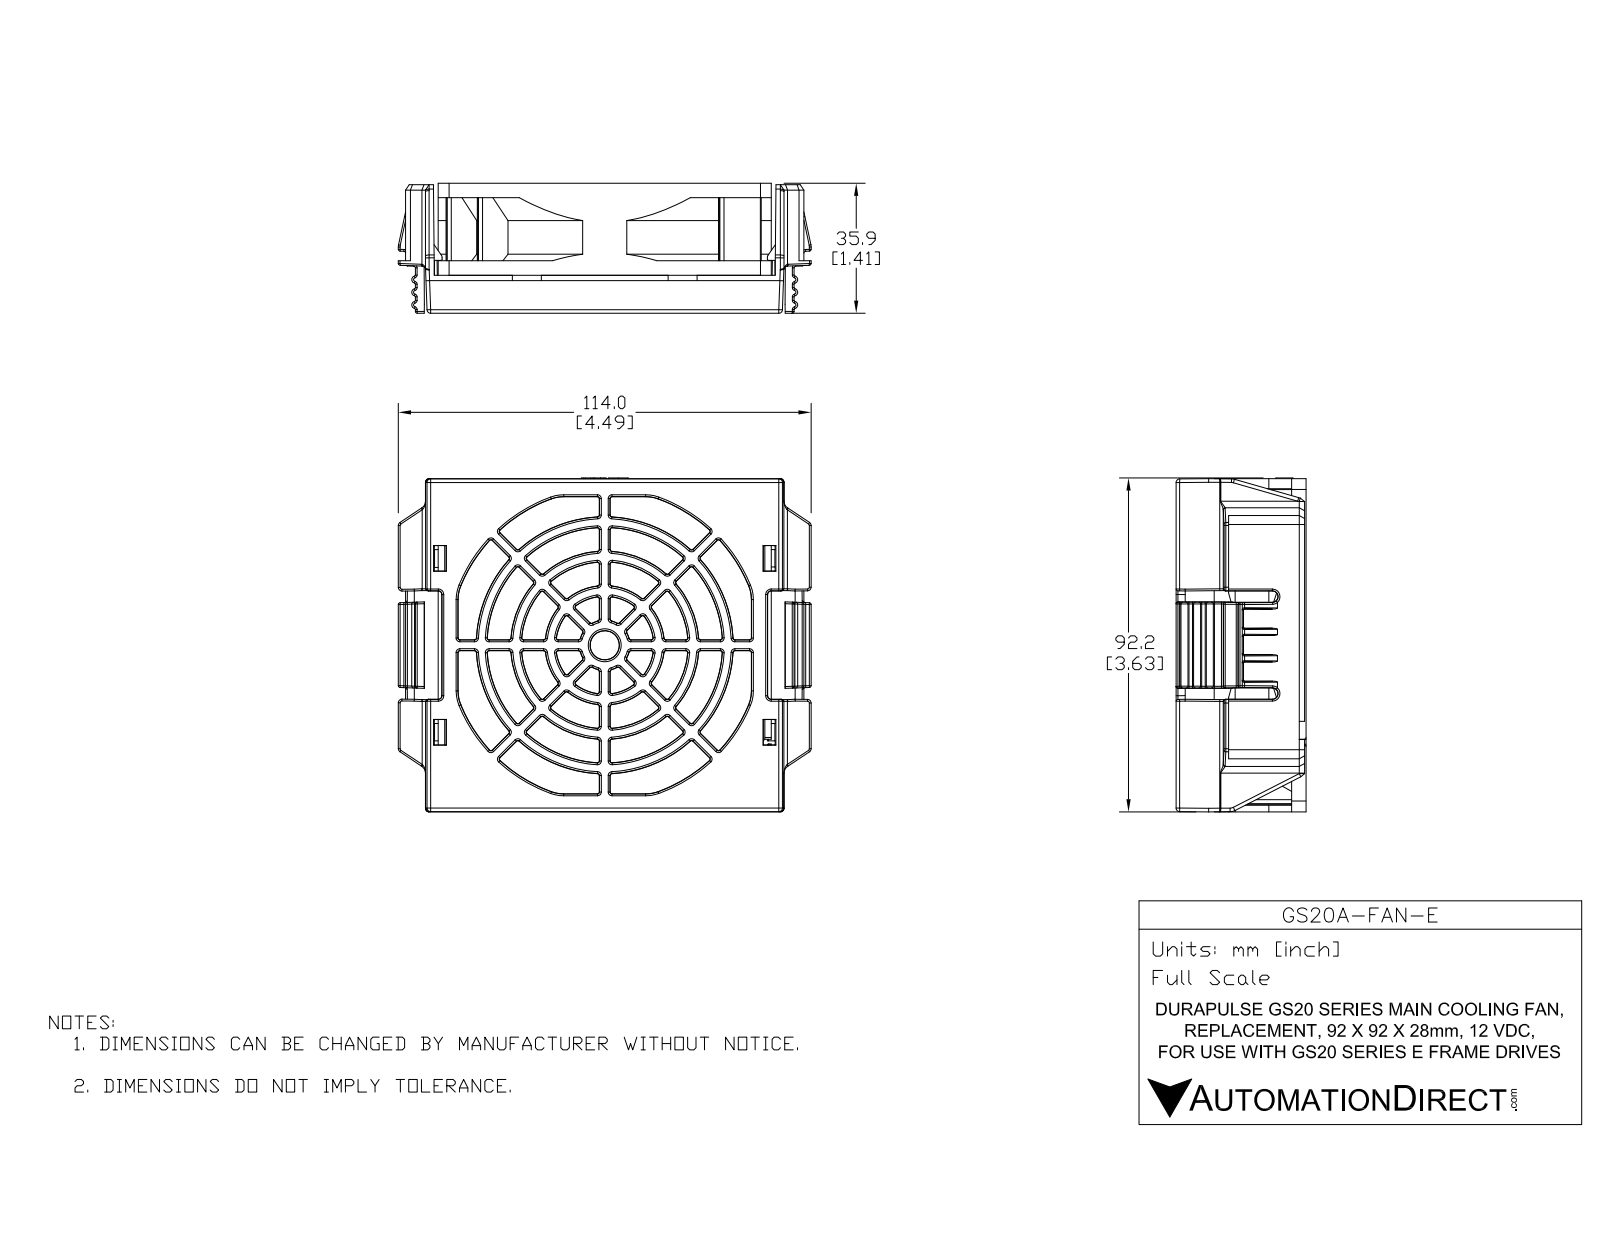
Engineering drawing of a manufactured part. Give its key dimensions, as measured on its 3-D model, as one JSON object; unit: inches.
{"part_name": "GS20A-FAN-E", "step_written_by": "SolidWorks 2017 (AUTOMOTIVE_DESIGN)", "units": "inches", "bodies": {"solids": 2, "faces": 2159, "planar": 685, "cylindrical": 535, "other": 939}, "overall_size": [4.488, 3.63, 1.413], "volume_in3": 12.56, "surface_area_in2": 105.9, "round_holes": [[0.165, 4], [0.048, 1]], "round_bosses_or_shafts": [[3.654, 1], [3.52, 1]], "partial_cylinders_radius": [[0.02, 142], [0.039, 46], [0.012, 40], [0.031, 16], [0.118, 12], [0.016, 4], [0.038, 4], [0.049, 4]], "face_to_face_distances": [0.945, 1.315, 0.37, 1.413, 0.469, 0.098, 3.622, 0.071, 0.354, 0.843], "hole_center_spacings": [3.248, 4.593]}
